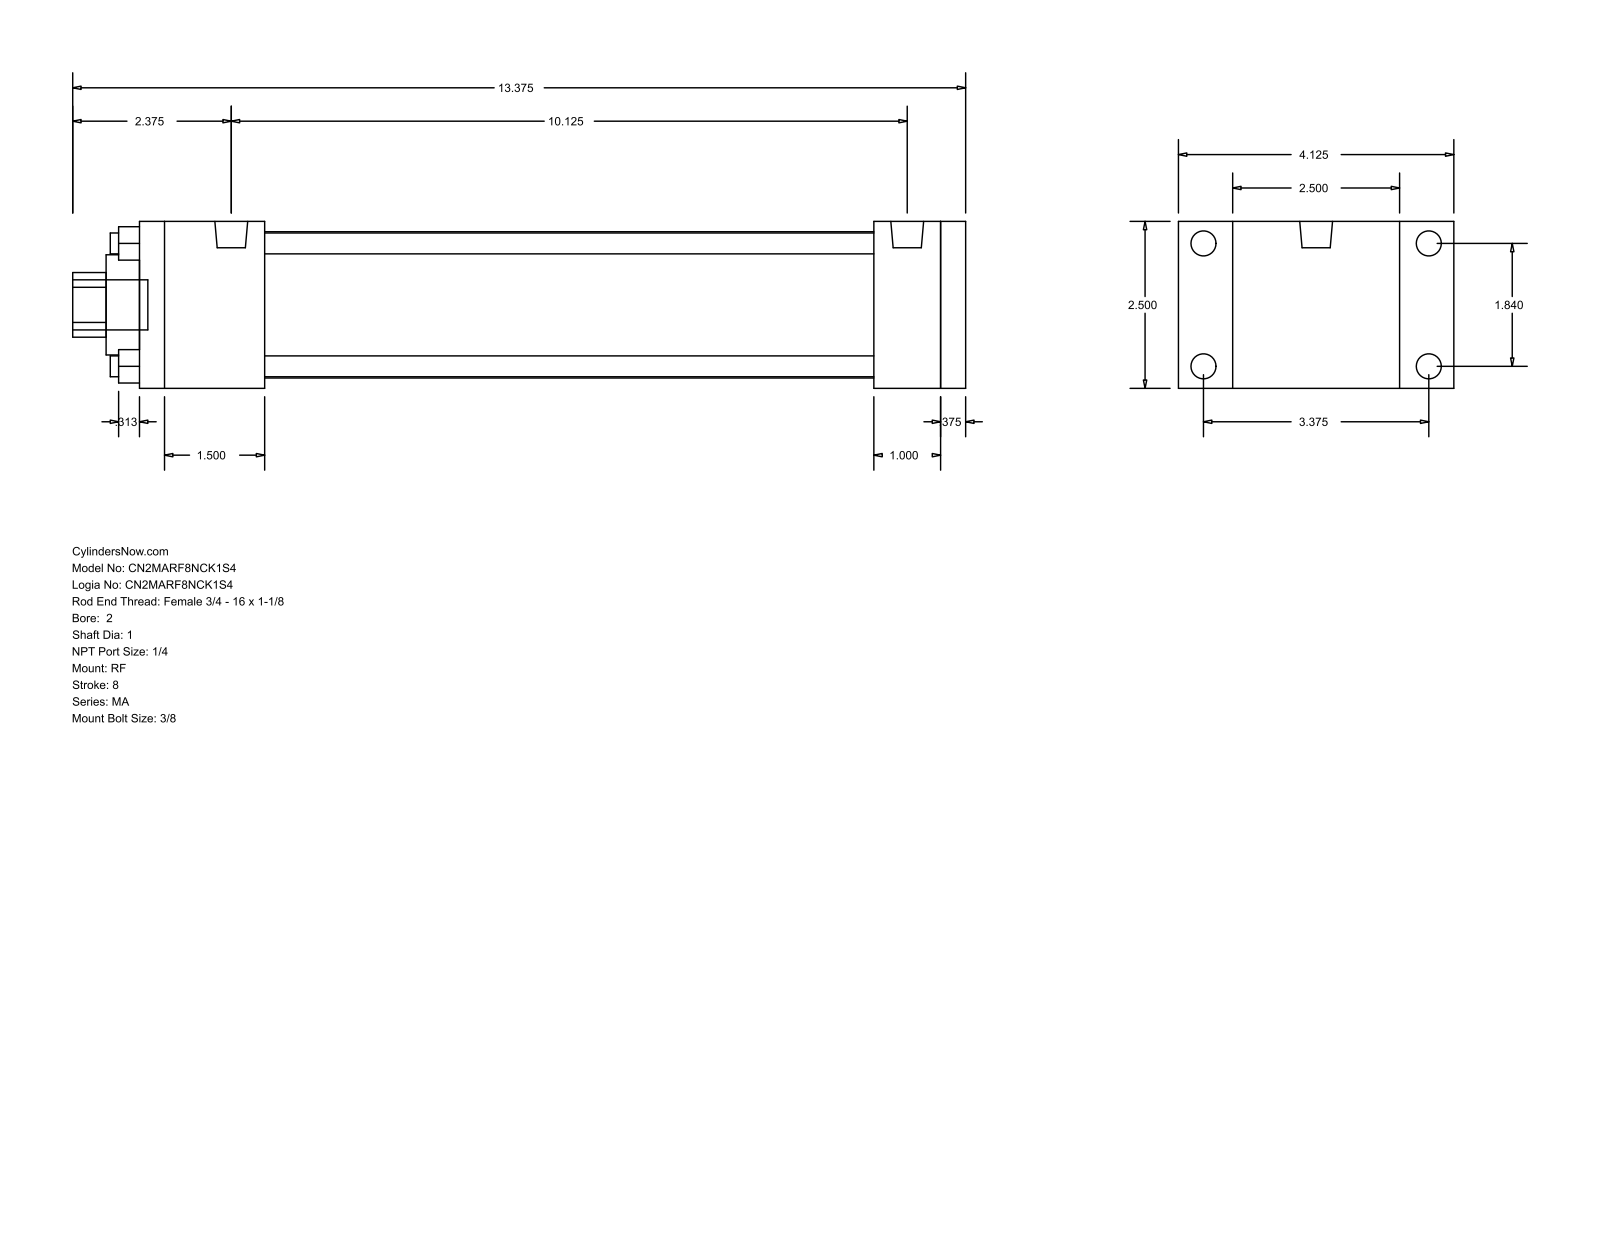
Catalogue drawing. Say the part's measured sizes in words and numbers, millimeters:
The part is named "MA_RF__0200_1". Its 3-D file was written by "GSSL Pune (CONFIG_CONTROL_DESIGN)". It is 0 solids with 92 faces: 64 planar, 28 cylindrical and 0 other. Overall it measures 339.73 by 104.78 by 63.5 millimeters. Round holes: 4 of diameter 7.94, 1 of diameter 25.4, 1 of diameter 38.1, 1 of diameter 55.63. Round bosses or shafts: 4 of diameter 9.53, 4 of diameter 7.94, 2 of diameter 12.49, 1 of diameter 19.05. Partial cylindrical surfaces (rounded edges, fillets, slot ends): 1 of radius 12.29. The main face-to-face distances are 63.5, 304.8, 9.53, 314.33, 25.4, 20.64, 12.7, 47.63, 257.17, 266.7. The hole center spacings are 33.05, 46.74, 66.1.
